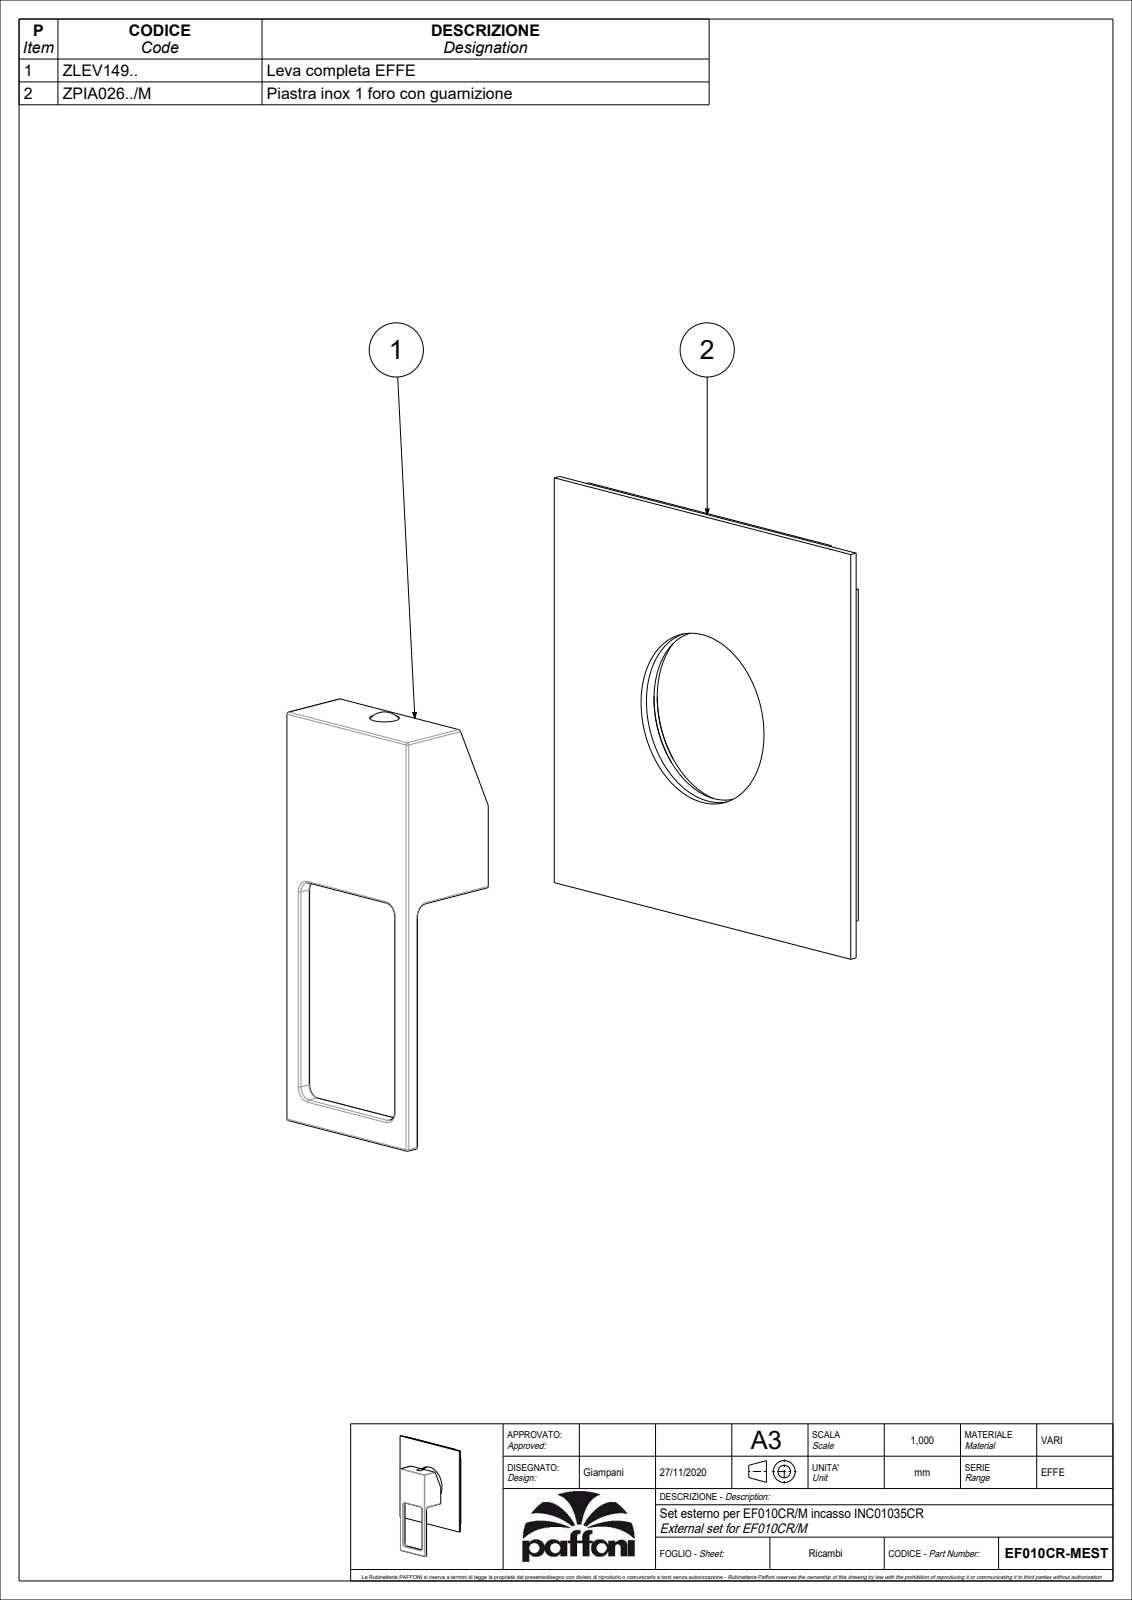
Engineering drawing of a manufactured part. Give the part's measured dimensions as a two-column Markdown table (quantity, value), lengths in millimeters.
| quantity | value |
| --- | --- |
| part name | EF010CR-MEST |
| STEP written by | CREO PARAMETRIC BY PTC INC, 2020044 (CONFIG_CONTROL_DESIGN) |
| units | millimeters |
| bodies | 2 solids, 169 faces (82 planar, 57 cylindrical, 30 other) |
| overall size | 143.5 × 110 × 39.5 |
| volume | 43 643 mm³ |
| surface area | 43 073 mm² |
| round holes (diameter × count) | 3 × 1, 4.5 × 1, 5.5 × 1, 7.8 × 1, 45.6 × 1, 47.6 × 1, 51.1 × 1 |
| round bosses / shafts (diameter × count) | 54.6 × 1, 7.6 × 1, 5 × 1 |
| partial cylindrical surfaces (radius × count) | 0.5 × 20, 3 × 5, 4 × 1 |
| main face-to-face distances | 2, 0.8, 2.8, 34.8, 34, 32, 45, 3, 31.8, 31 |
